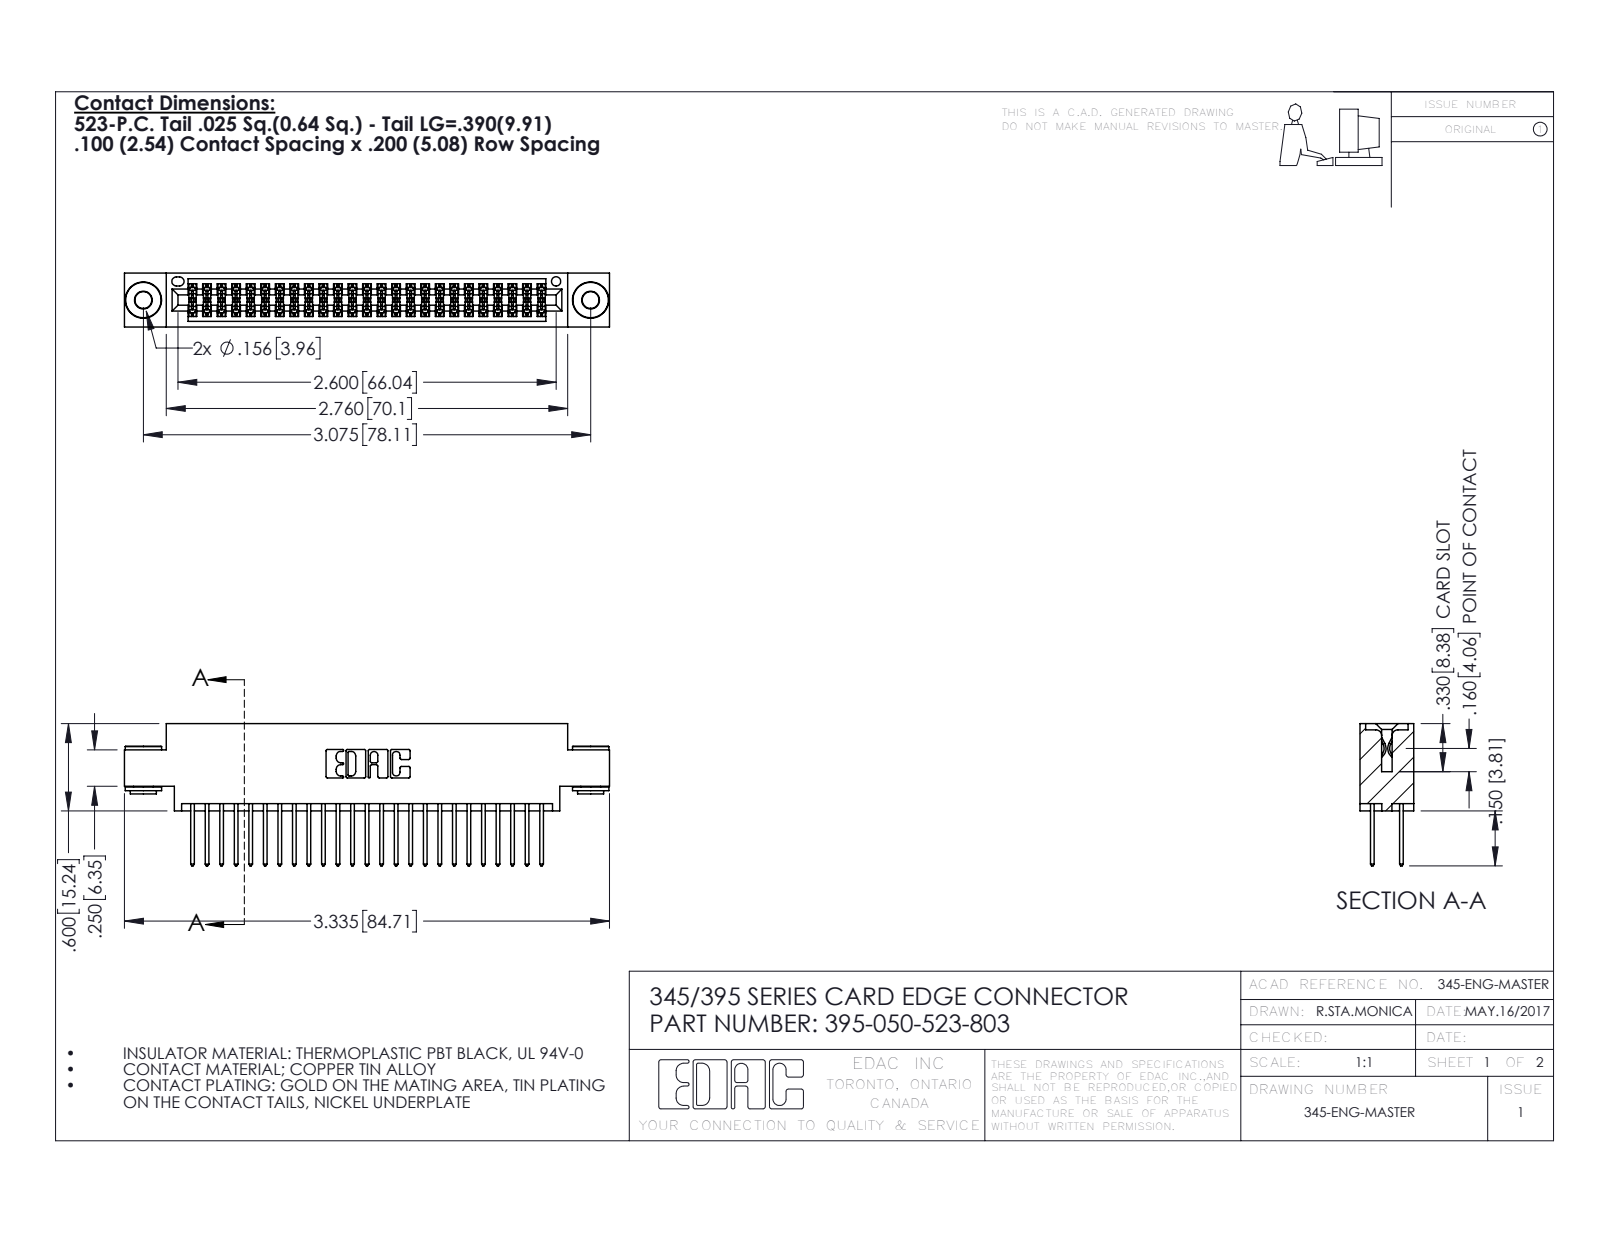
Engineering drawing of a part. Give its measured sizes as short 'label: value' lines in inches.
name: 345-250-002_345-250-002-102; 345 Part_0.170 Offset - 0.156 Dia-TH; 395-050-523-803; 345-292-001_345-293-123
written by: SolidWorks 2016 (CONFIG_CONTROL_DESIGN)
unit: in
bodies: 53 solids, 2668 faces (1744 planar, 916 cylindrical, 8 other)
size: 3.335 × 0.977 × 0.37
volume: 0.493 in³; area: 19.25 in²
holes: 2× ⌀0.116, 2× ⌀0.156, 1× ⌀0.064
bosses: 2× ⌀0.25, 2× ⌀0.18, 2× ⌀0.136
rounds: 75× R0.006, 50× R0.01, 22× R0.01, 6× R0.007, 6× R0.031, 3× R0.026, 2× R0.014, 2× R0.019
face distances: 0.072, 0.298, 0.2, 0.37, 0.098, 0.272, 0.025, 0.225, 0.175, 0.149
hole spacings: 0.27, 2.84, 3.075
